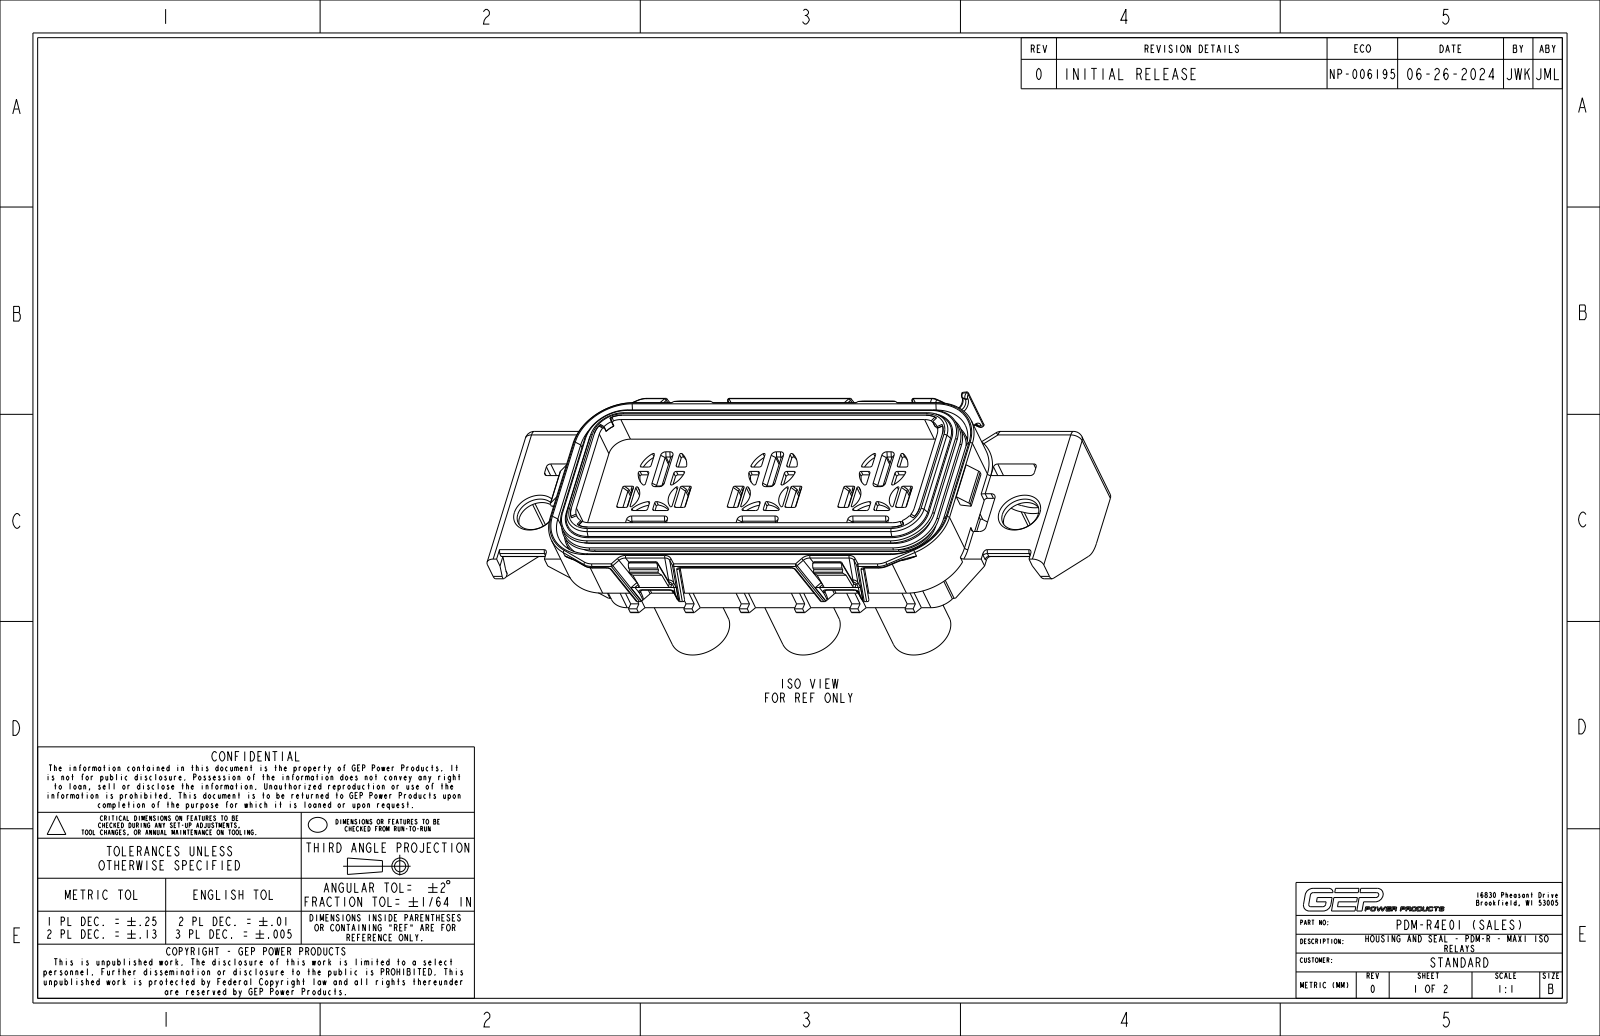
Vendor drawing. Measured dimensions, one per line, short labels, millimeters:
name: C26-1012-2E_SALES_NCF; C14-1013_INSTALLED_NCF; PDM-RS_INSTALLED_NCF_ASM; PDM-R4E01_NCF_ASM
written by: CREO PARAMETRIC BY PTC INC, 2024014 (CONFIG_CONTROL_DESIGN)
unit: mm
bodies: 2 solids, 2811 faces (1356 planar, 832 cylindrical, 623 other)
size: 163 × 60.76 × 56
volume: 119 268 mm³; area: 104 850 mm²
holes: 6× ⌀9.8, 6× ⌀13.75, 4× ⌀10.5, 2× ⌀12.5
bosses: 3× ⌀16.75, 1× ⌀5, 1× ⌀2.5
rounds: 237× R0.5, 82× R0.3, 76× R0.4, 40× R0.2, 39× R0.9, 26× R1, 24× R0.6, 16× R0.35
face distances: 1.5, 2, 38.5, 37, 9.5, 1.8, 11.5, 5.5, 9, 7
hole spacings: 32.4, 12.47, 13.24, 24.66, 25.05, 37.02, 42.46, 42.69
